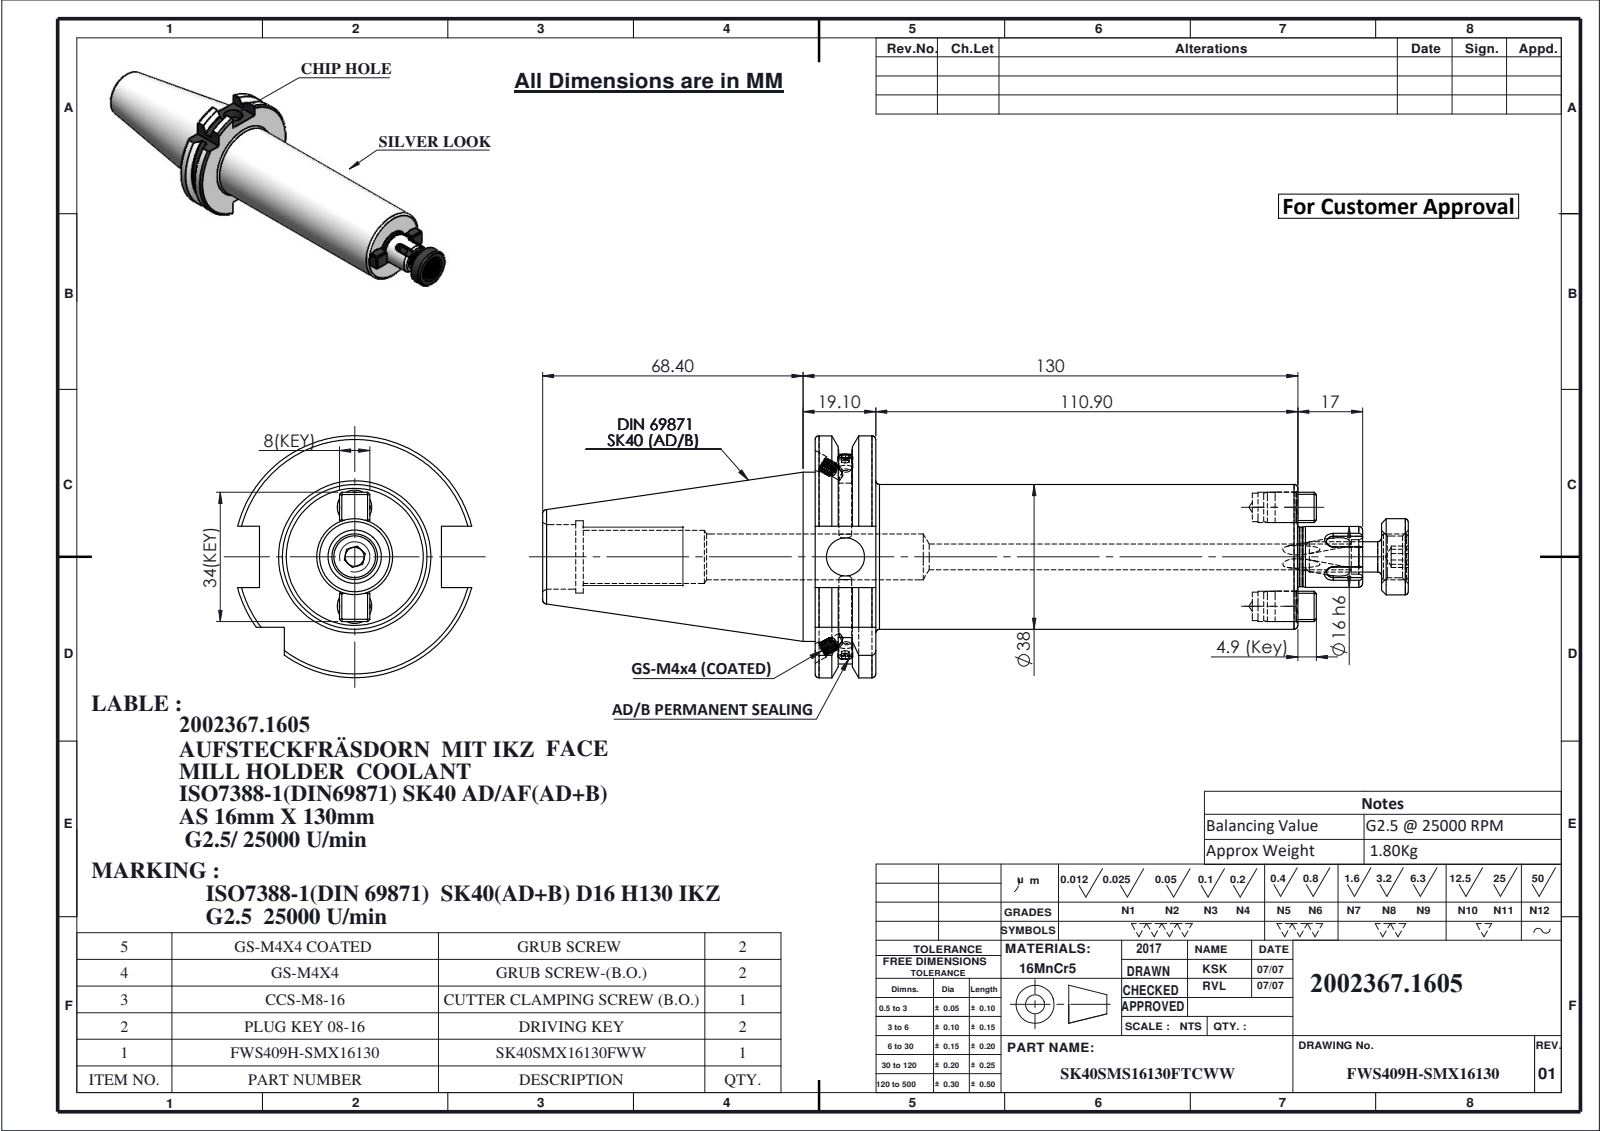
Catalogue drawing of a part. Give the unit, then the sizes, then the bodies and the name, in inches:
Units: inches
Overall size (bounding box): 8.953 × 2.502 × 2.42
Round holes (diameter × count): ⌀0.118 ×4, ⌀0.13 ×3, ⌀0.177 ×2, ⌀0.295 ×2, ⌀0.315 ×2, ⌀0.268 ×1, ⌀0.354 ×1, ⌀0.394 ×1, ⌀0.433 ×1, ⌀0.472 ×1, ⌀0.551 ×1, ⌀0.669 ×1
Round bosses / shafts (diameter × count): ⌀0.157 ×4, ⌀0.316 ×2, ⌀0.314 ×2, ⌀0.114 ×2, ⌀1.75 ×1, ⌀1.496 ×1, ⌀0.787 ×1, ⌀0.63 ×1
Partial cylindrical surfaces — rounded edges, fillets, slot ends (radius × count): R0.079 ×4, R0.207 ×2, R1.107 ×1, R1.251 ×1
Main face-to-face distances: 0.626, 4.992, 4.366, 1.142, 6.134, 5.508, 0.634, 1.882, 0.472, 1.024
Hole centre spacings: 0.512, 1.024
Volume: 13.83 in³ · Surface area: 65.58 in²
Bodies: 9 solids, 430 faces (131 planar, 122 cylindrical, 177 other)
Part name (STEP PRODUCT): CCS-M8-16; M4X4_DIN 913 - M4 x 4-N; GS-M4X4-COATING_DIN 913 - M4 x 4-N; SK40SMX16130FWW (+4 more)
STEP written by: SolidWorks 2024 (CONFIG_CONTROL_DESIGN)
